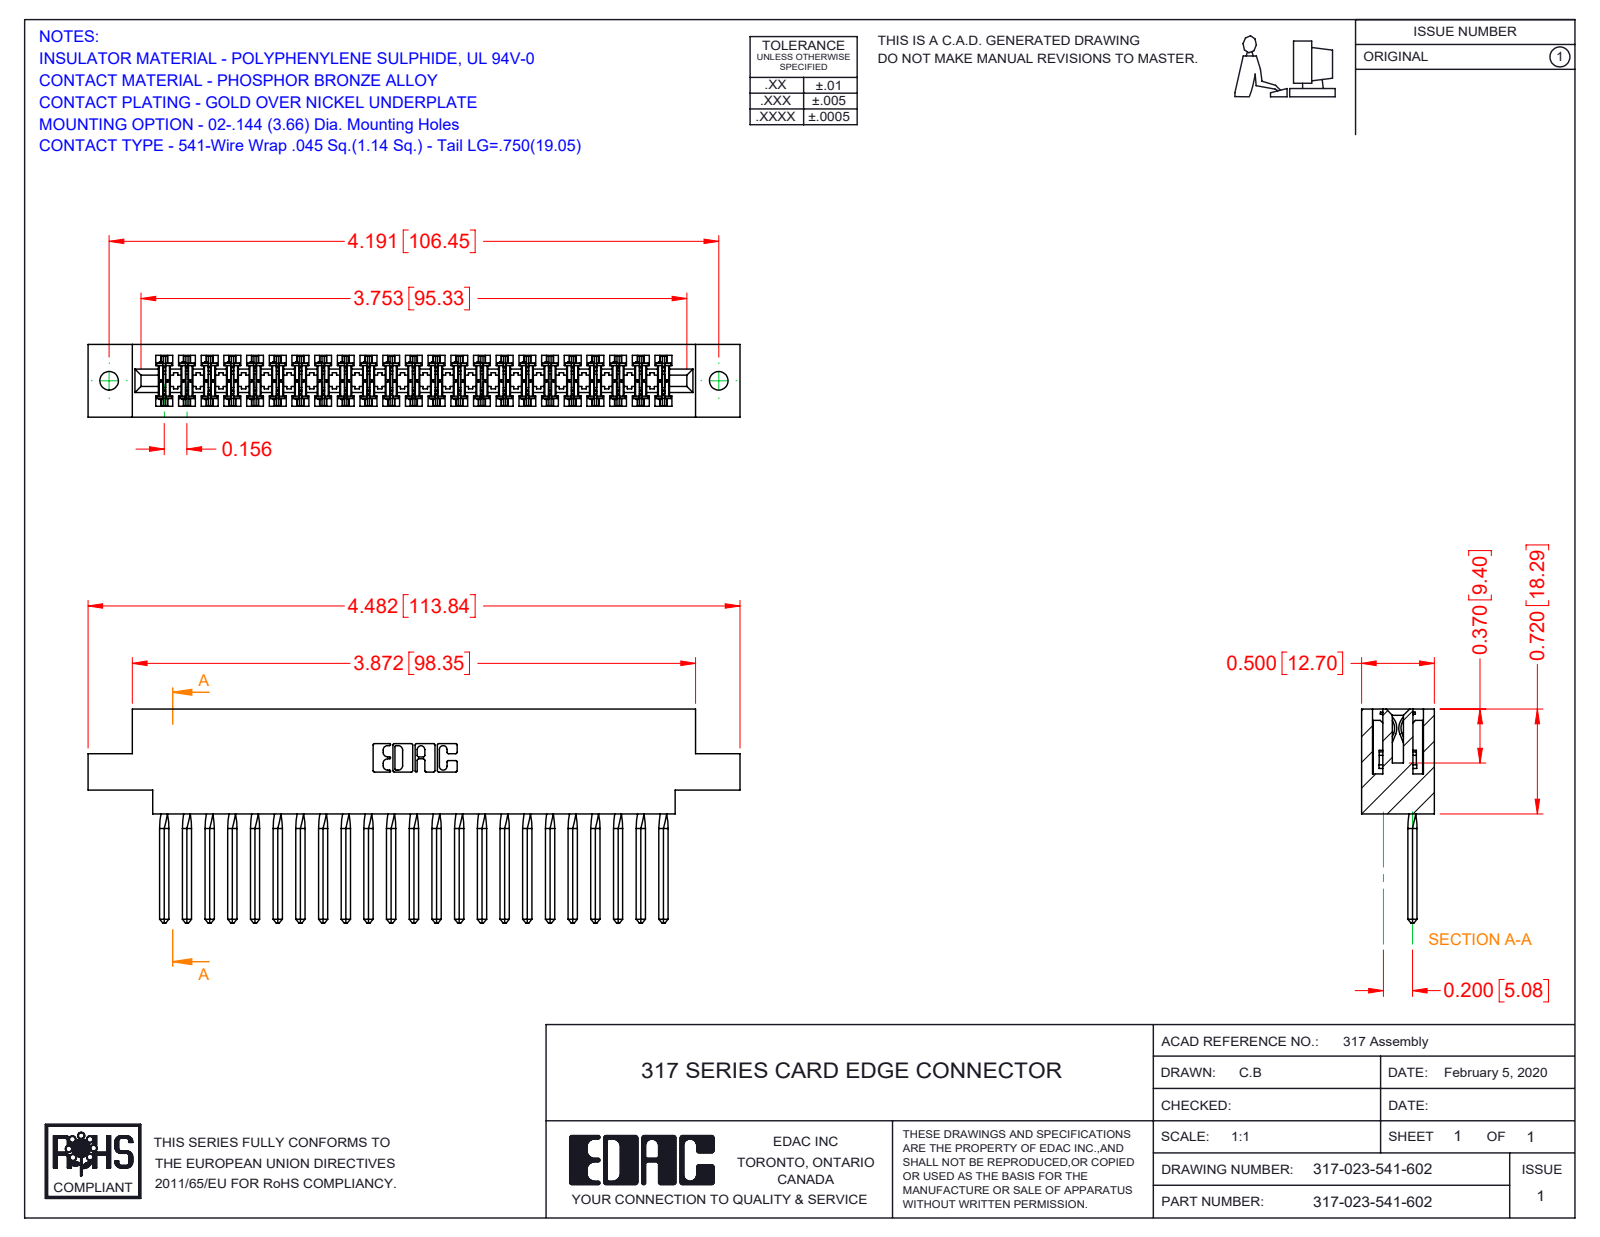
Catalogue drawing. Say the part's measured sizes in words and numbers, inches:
The part is named "317 Part_.144 Dia; 317-023-541-602; 317-290-002_541". Its 3-D file was written by "SolidWorks 2016 (CONFIG_CONTROL_DESIGN)". It is 24 solids with 3598 faces: 2910 planar, 596 cylindrical and 92 other. Overall it measures 4.482 by 1.47 by 0.5 inches. Its volume is 1.089 cubic inches and its surface area 37.68 square inches. Round holes: 2 of diameter 0.128. Partial cylindrical surfaces (rounded edges, fillets, slot ends): 46 of radius 0.015, 22 of radius 0.01, 6 of radius 0.007, 6 of radius 0.031, 3 of radius 0.026, 2 of radius 0.095, 2 of radius 0.1, 2 of radius 0.11. The main face-to-face distances are 0.5, 0.075, 0.425, 0.11, 0.35, 0.195, 0.772, 0.22, 0.72, 0.662. The hole center spacings are 4.191.
